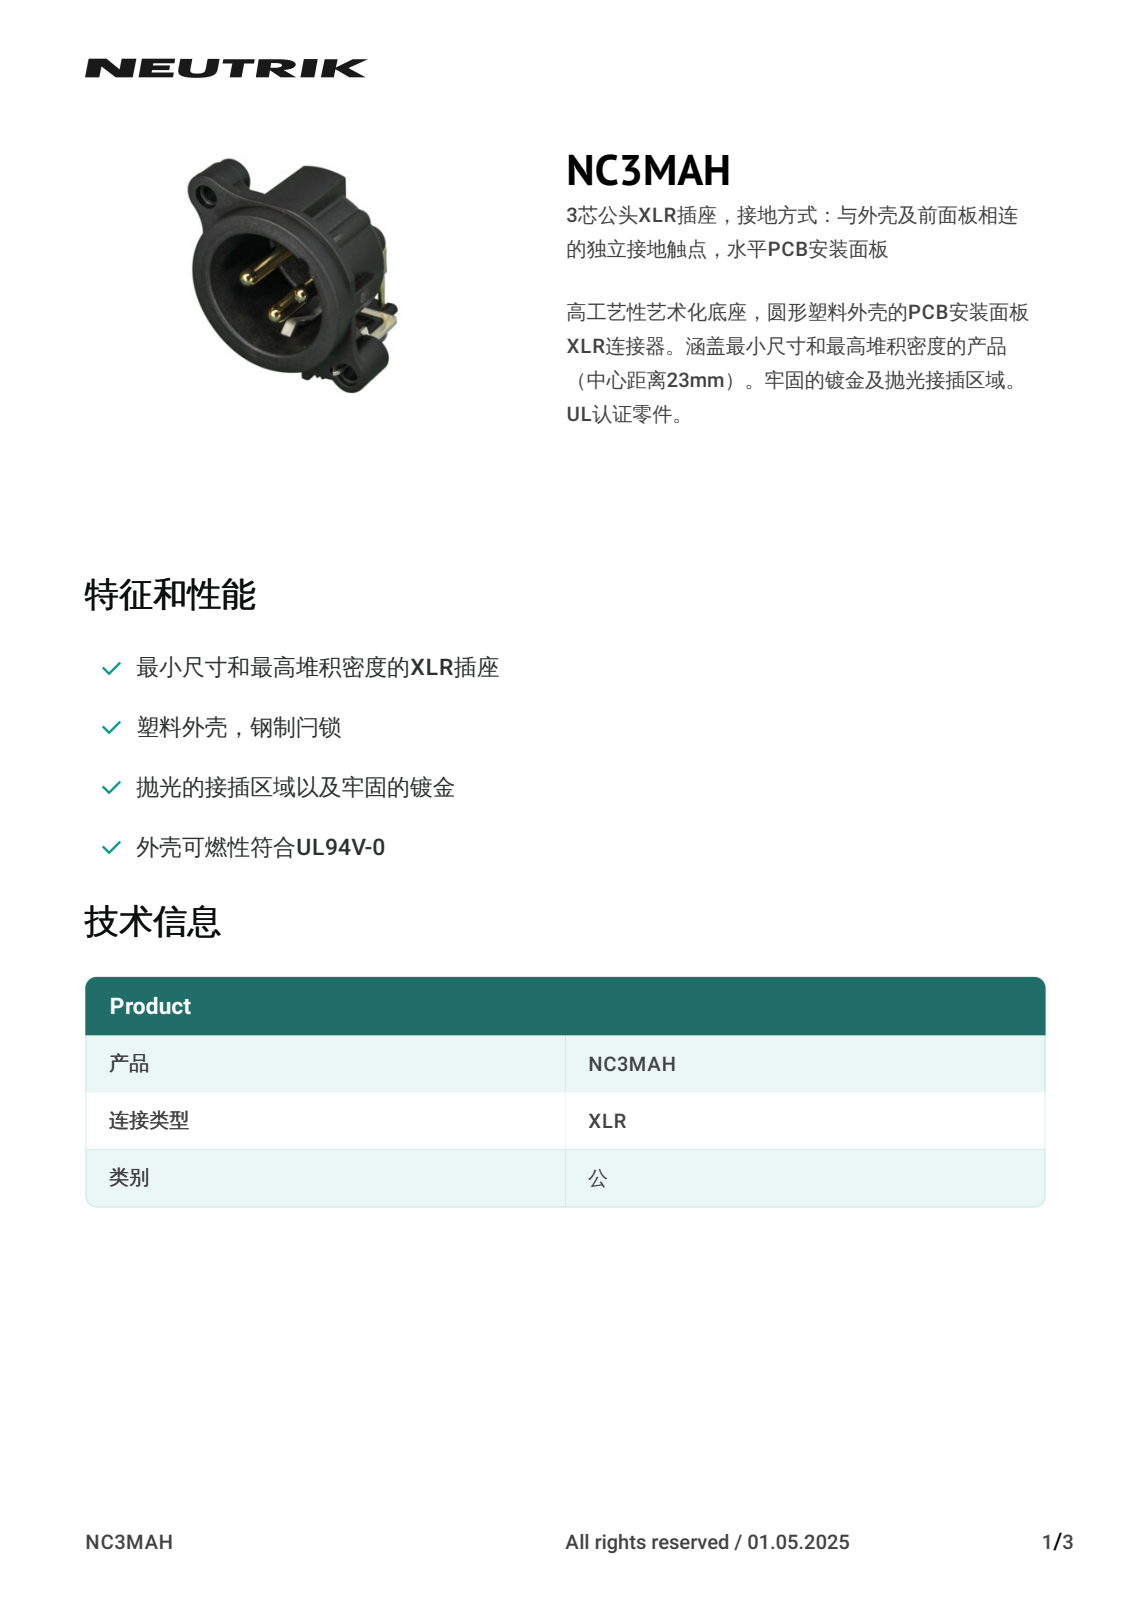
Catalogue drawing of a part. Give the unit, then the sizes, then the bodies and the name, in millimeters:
Units: millimetres
Overall size (bounding box): 39.69 × 28.9 × 25.3
Round holes (diameter × count): ⌀1.84 ×3, ⌀2.3 ×2, ⌀2.5 ×1, ⌀3.2 ×1
Round bosses / shafts (diameter × count): ⌀1.5 ×5, ⌀2.38 ×3, ⌀1.8 ×3, ⌀1.6 ×3, ⌀1.2 ×3, ⌀0.9 ×3, ⌀21.8 ×1, ⌀5.8 ×1
Partial cylindrical surfaces — rounded edges, fillets, slot ends (radius × count): R0.3 ×71, R0.2 ×26, R0.5 ×12, R0.12 ×9, R1 ×6, R0.75 ×3, R1.5 ×3, R0.19 ×2
Main face-to-face distances: 1, 13.4, 14.4, 10.7, 0.5, 2.7, 1.28, 11.7, 3.7, 9.7
Hole centre spacings: 5.66, 6.67, 11.5, 17.11, 8.1, 9.25, 10.92, 11.55
Volume: 2 517 mm³ · Surface area: 4 792 mm²
Bodies: 1 solid, 1039 faces (428 planar, 245 cylindrical, 366 other)
Part name (STEP PRODUCT): NC3MAH
STEP written by: CREO PARAMETRIC BY PTC INC, 2023424 (AUTOMOTIVE_DESIGN)
